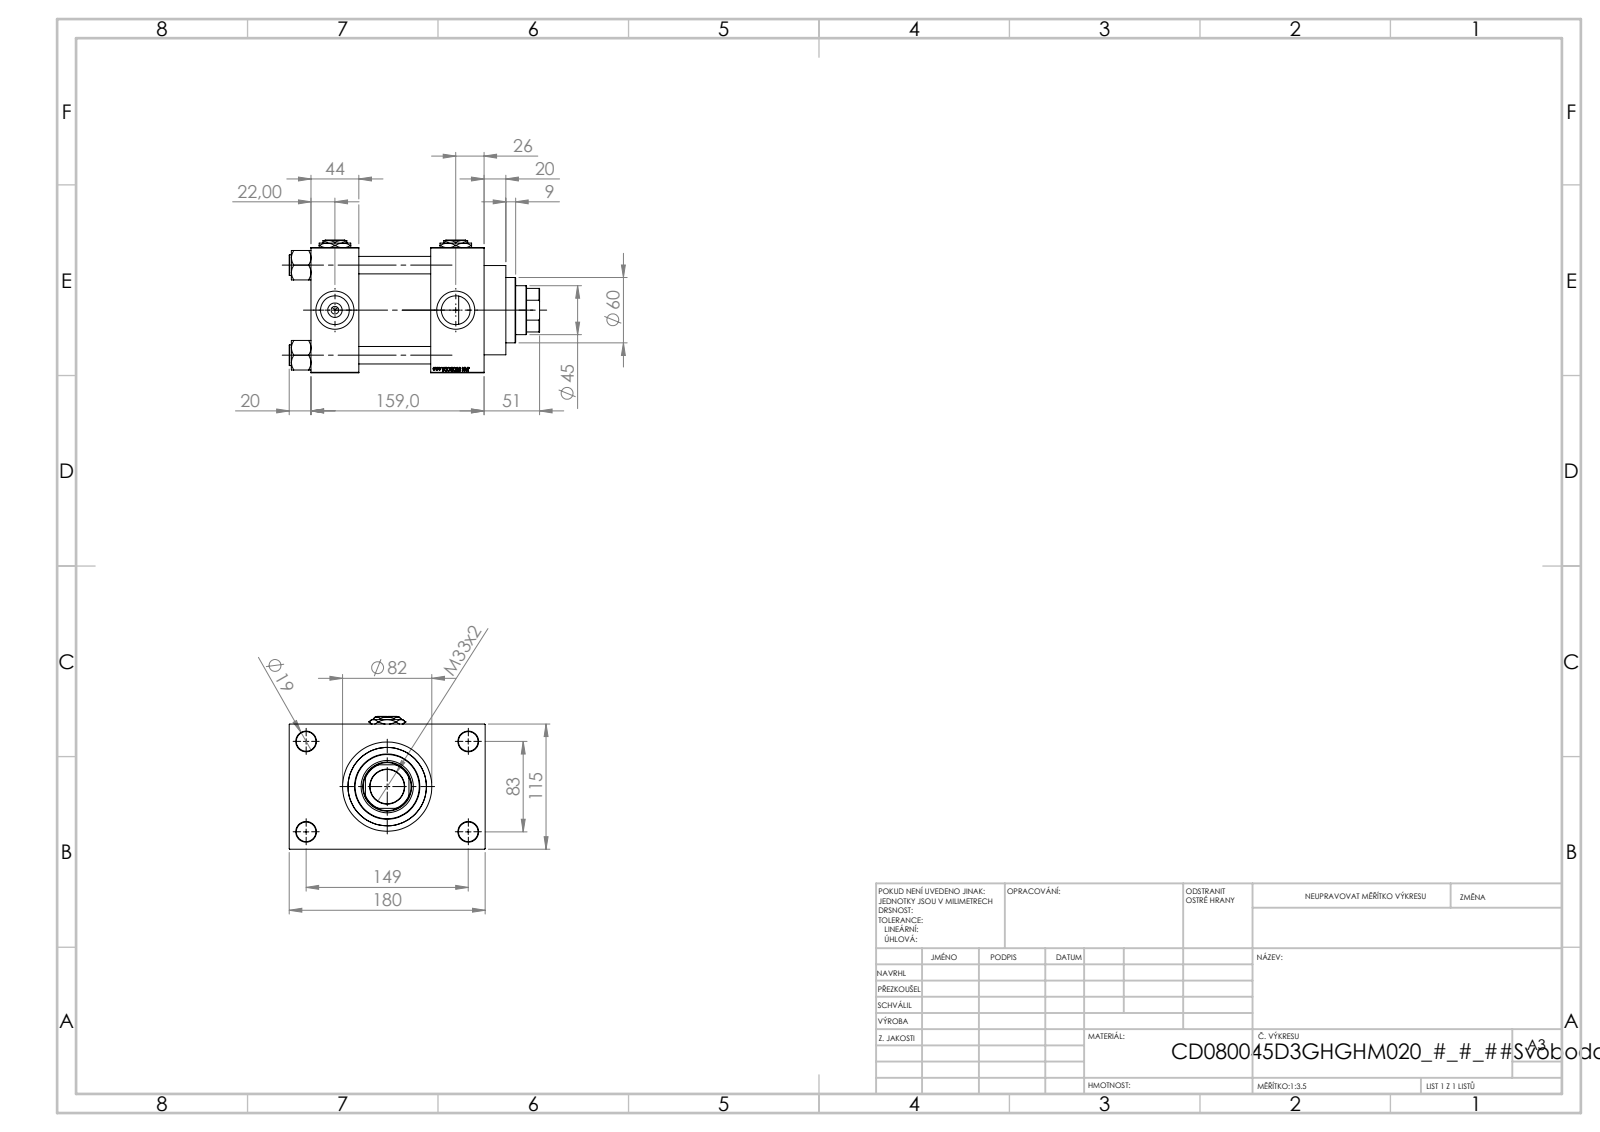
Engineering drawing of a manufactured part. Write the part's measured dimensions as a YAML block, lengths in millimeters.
part_name: "V215CD_NUT_M5_D; V215CD_D_TYCINKA; V215CD_D_Body; Zatka_pro_OIL_PORT (+2 more)"
step_written_by: "SolidWorks 2019 (CONFIG_CONTROL_DESIGN)"
units: millimeters
bodies: {solids: 13, faces: 1252, planar: 593, cylindrical: 99, other: 560}
overall_size: [230, 180, 122]
volume: 1990000
surface_area: 309159
round_holes:
  - {diameter: 16, count: 4}
  - {diameter: 18, count: 4}
  - {diameter: 26.44, count: 4}
  - {diameter: 35, count: 4}
  - {diameter: 7, count: 3}
  - {diameter: 31.5, count: 1}
  - {diameter: 45, count: 1}
  - {diameter: 48, count: 1}
  - {diameter: 61, count: 1}
  - {diameter: 72, count: 1}
  - {diameter: 80, count: 1}
round_bosses_or_shafts:
  - {diameter: 19, count: 4}
  - {diameter: 86, count: 1}
  - {diameter: 82, count: 1}
  - {diameter: 60, count: 1}
partial_cylinders:
  - {radius: 22, count: 1}
face_to_face_distances: [115, 110, 66, 49, 44, 159, 32.5, 147.5, 20, 69]
hole_center_spacings: [33.15, 58.48, 82.7, 85.28, 89.24, 115.85, 142.43, 83]
